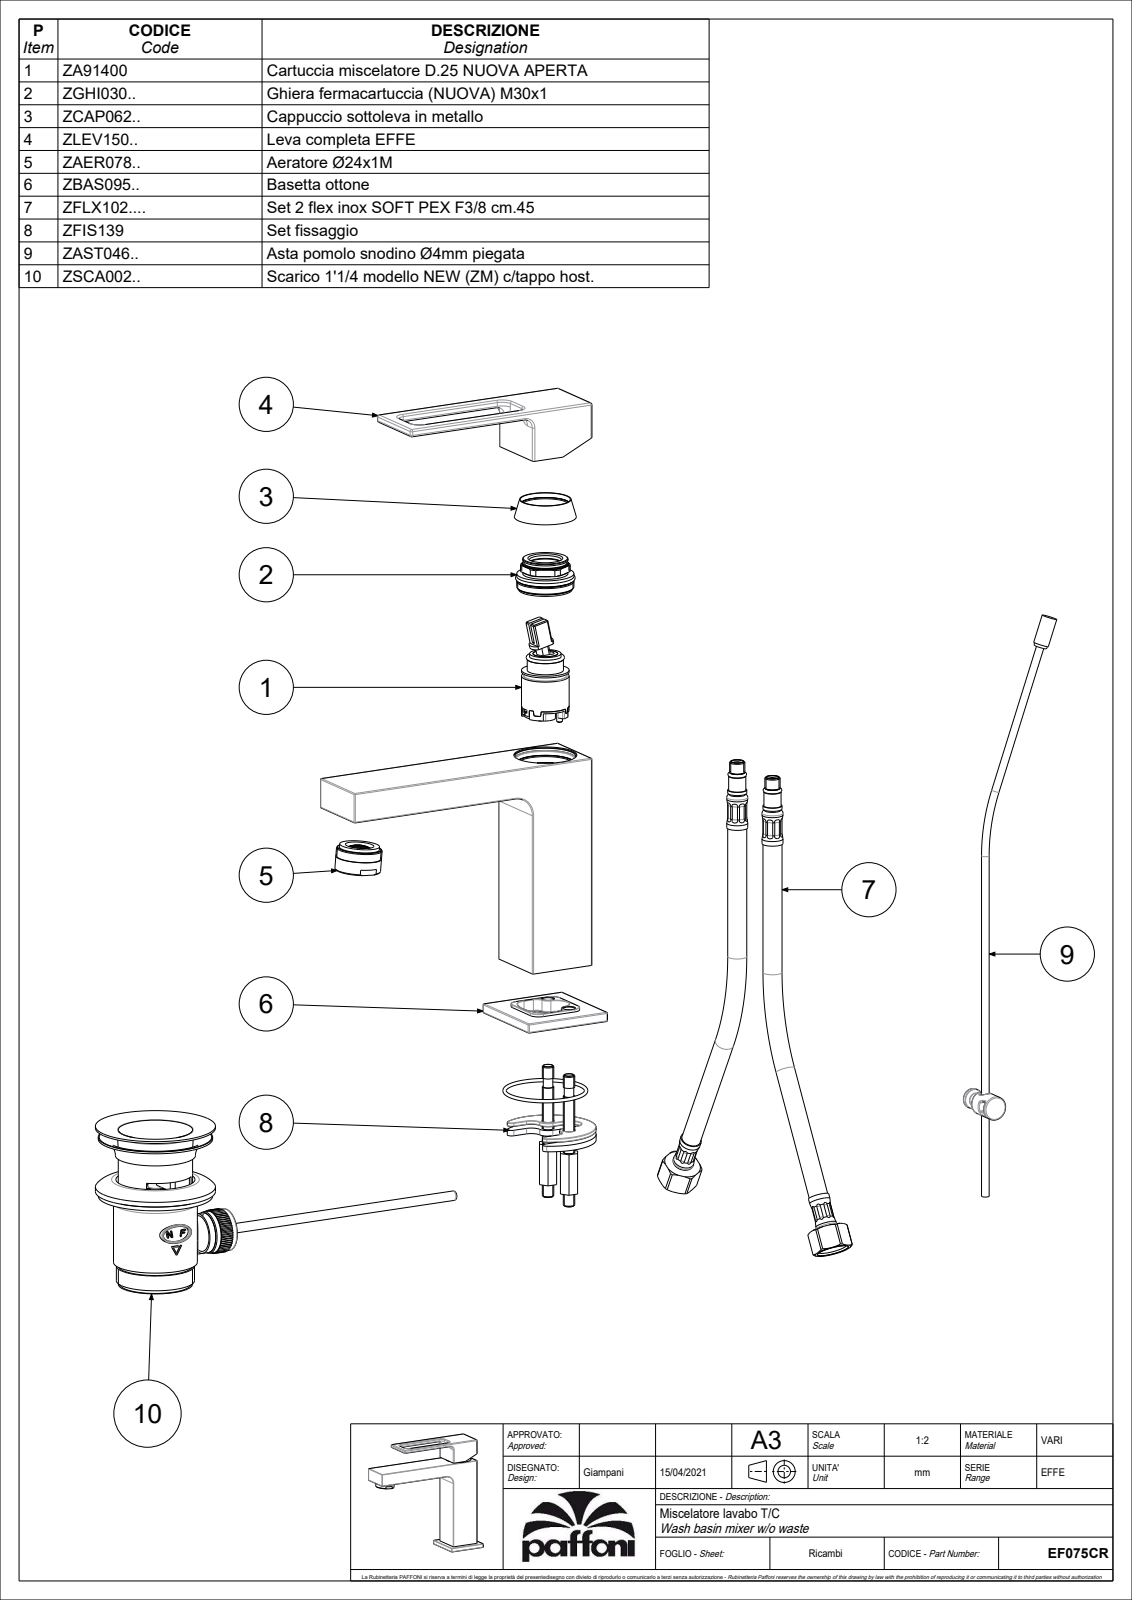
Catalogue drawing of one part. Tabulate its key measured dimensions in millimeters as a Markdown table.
| quantity | value |
| --- | --- |
| part name | EF075CR |
| STEP written by | CREO PARAMETRIC BY PTC INC, 2020044 (CONFIG_CONTROL_DESIGN) |
| units | millimeters |
| bodies | 5 solids, 1927 faces (1547 planar, 218 cylindrical, 162 other) |
| overall size | 158.1 × 145.58 × 48 |
| volume | 119 515 mm³ |
| surface area | 75 774 mm² |
| round holes (diameter × count) | 5.5 × 3, 6.2 × 2, 3 × 1, 4.2 × 1, 4.5 × 1, 5 × 1, 7.8 × 1, 16 × 1, 17 × 1, 20 × 1, 21 × 1, 23 × 1 |
| round bosses / shafts (diameter × count) | 41.8 × 1, 24 × 1, 19.5 × 1, 18.8 × 1, 16.8 × 1, 8 × 1, 7.6 × 1, 4 × 1 |
| partial cylindrical surfaces (radius × count) | 1 × 62, 0.5 × 27, 5 × 11, 1.5 × 8, 0.25 × 6, 4 × 6, 3.5 × 2, 7 × 2 |
| main face-to-face distances | 3, 36, 33, 13, 30, 16, 28.08, 41.08, 44.08, 31.08 |
| hole center spacings | 11.4, 13.6, 11, 22 |
